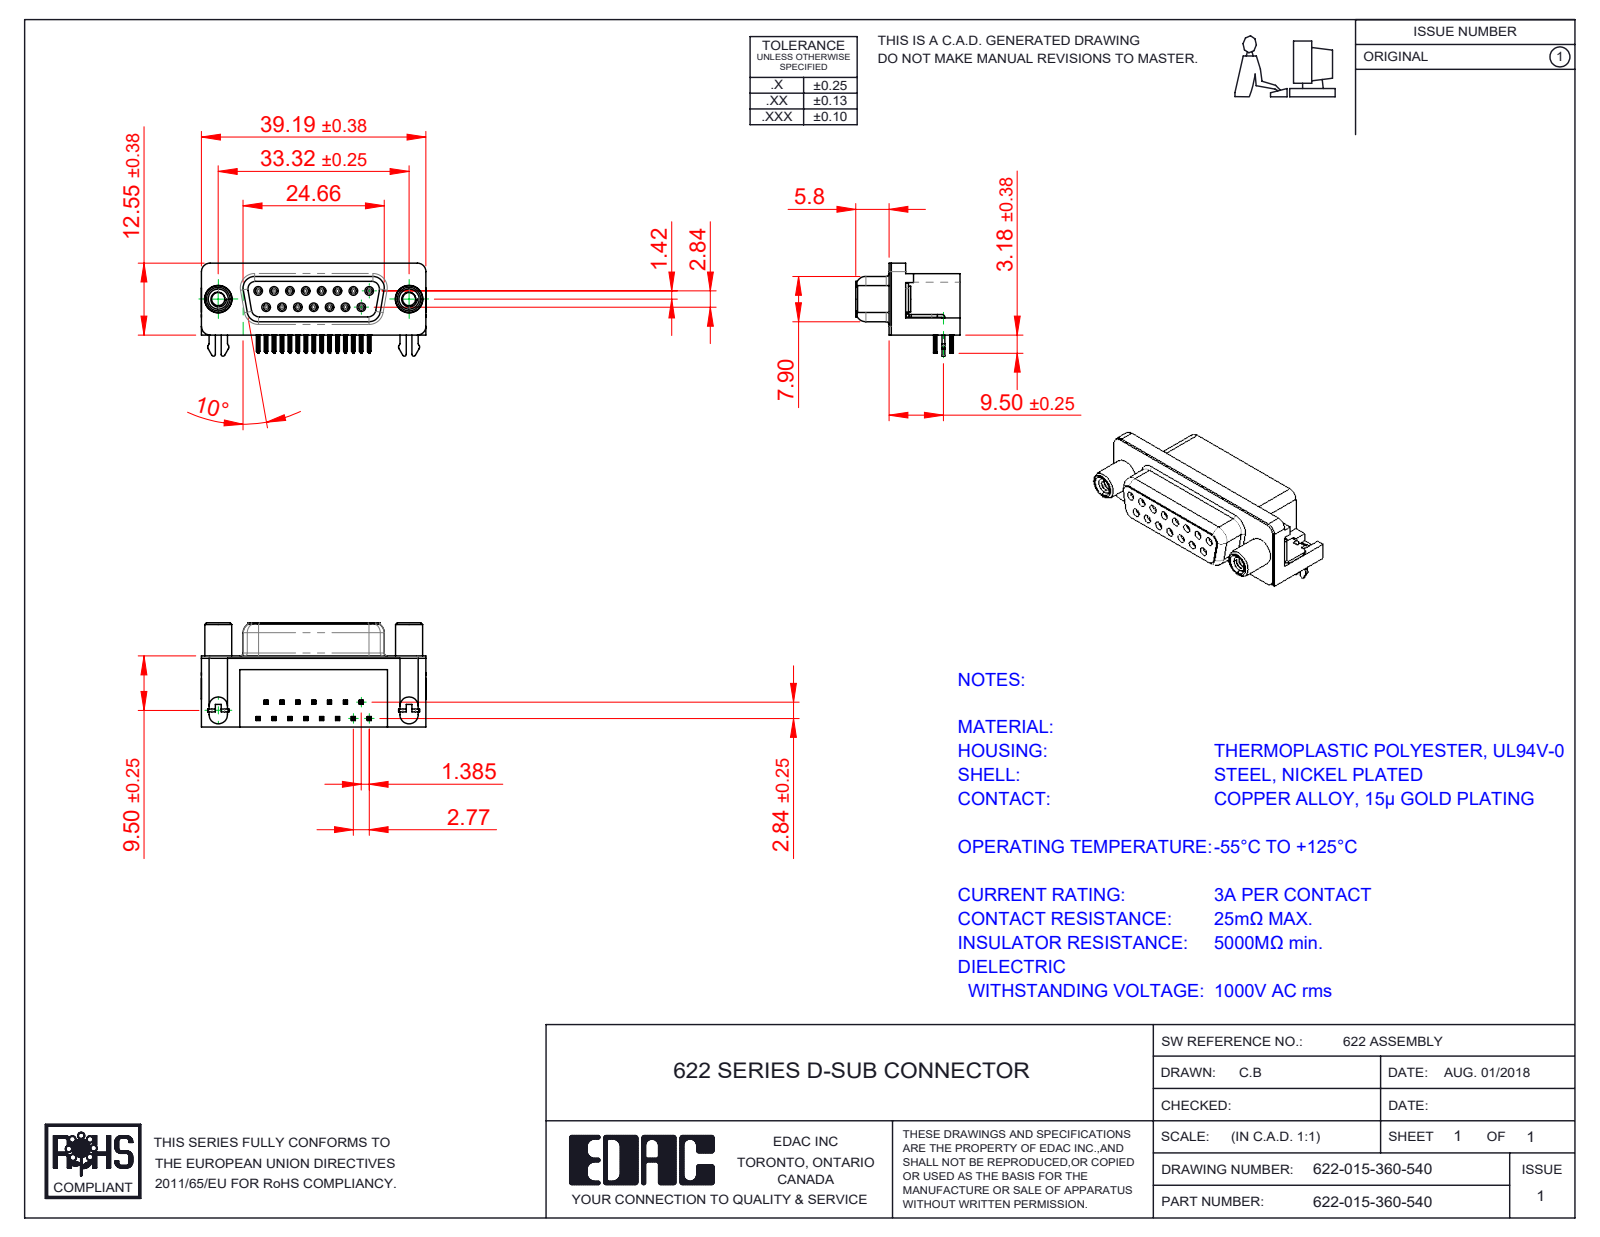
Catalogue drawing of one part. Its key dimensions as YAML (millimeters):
part_name: "622 4 Prong Board Lock; 622 Contact Top; 622 Round Threaded Standoff; 622 Housing_15 Socket (+3 more)"
step_written_by: "SolidWorks 2016 (CONFIG_CONTROL_DESIGN)"
units: millimeters
bodies: {solids: 21, faces: 2541, planar: 1108, cylindrical: 619, other: 814}
overall_size: [39.22, 18.2, 16.25]
volume: 5288
surface_area: 6990
round_holes:
  - {diameter: 0.8, count: 15}
  - {diameter: 0.9, count: 15}
  - {diameter: 2, count: 2}
  - {diameter: 2.3, count: 2}
  - {diameter: 3.1, count: 2}
  - {diameter: 4, count: 2}
  - {diameter: 4.8, count: 2}
  - {diameter: 5, count: 2}
round_bosses_or_shafts:
  - {diameter: 1.2, count: 15}
  - {diameter: 4.9, count: 2}
  - {diameter: 4.7, count: 2}
  - {diameter: 4.5, count: 2}
  - {diameter: 3.85, count: 2}
  - {diameter: 3, count: 2}
partial_cylinders:
  - {radius: 0.1, count: 120}
  - {radius: 0.15, count: 60}
  - {radius: 0.35, count: 30}
  - {radius: 1, count: 18}
  - {radius: 0.34, count: 15}
  - {radius: 1.35, count: 8}
  - {radius: 1.5, count: 8}
  - {radius: 1.6, count: 8}
face_to_face_distances: [0.4, 12, 6.2, 10.35, 12.4, 2.9, 6.65, 0.85, 0.35, 5.8]
hole_center_spacings: [3.16, 2.77, 5.54, 8.31, 11.08, 5.03, 5.04, 7.48]
